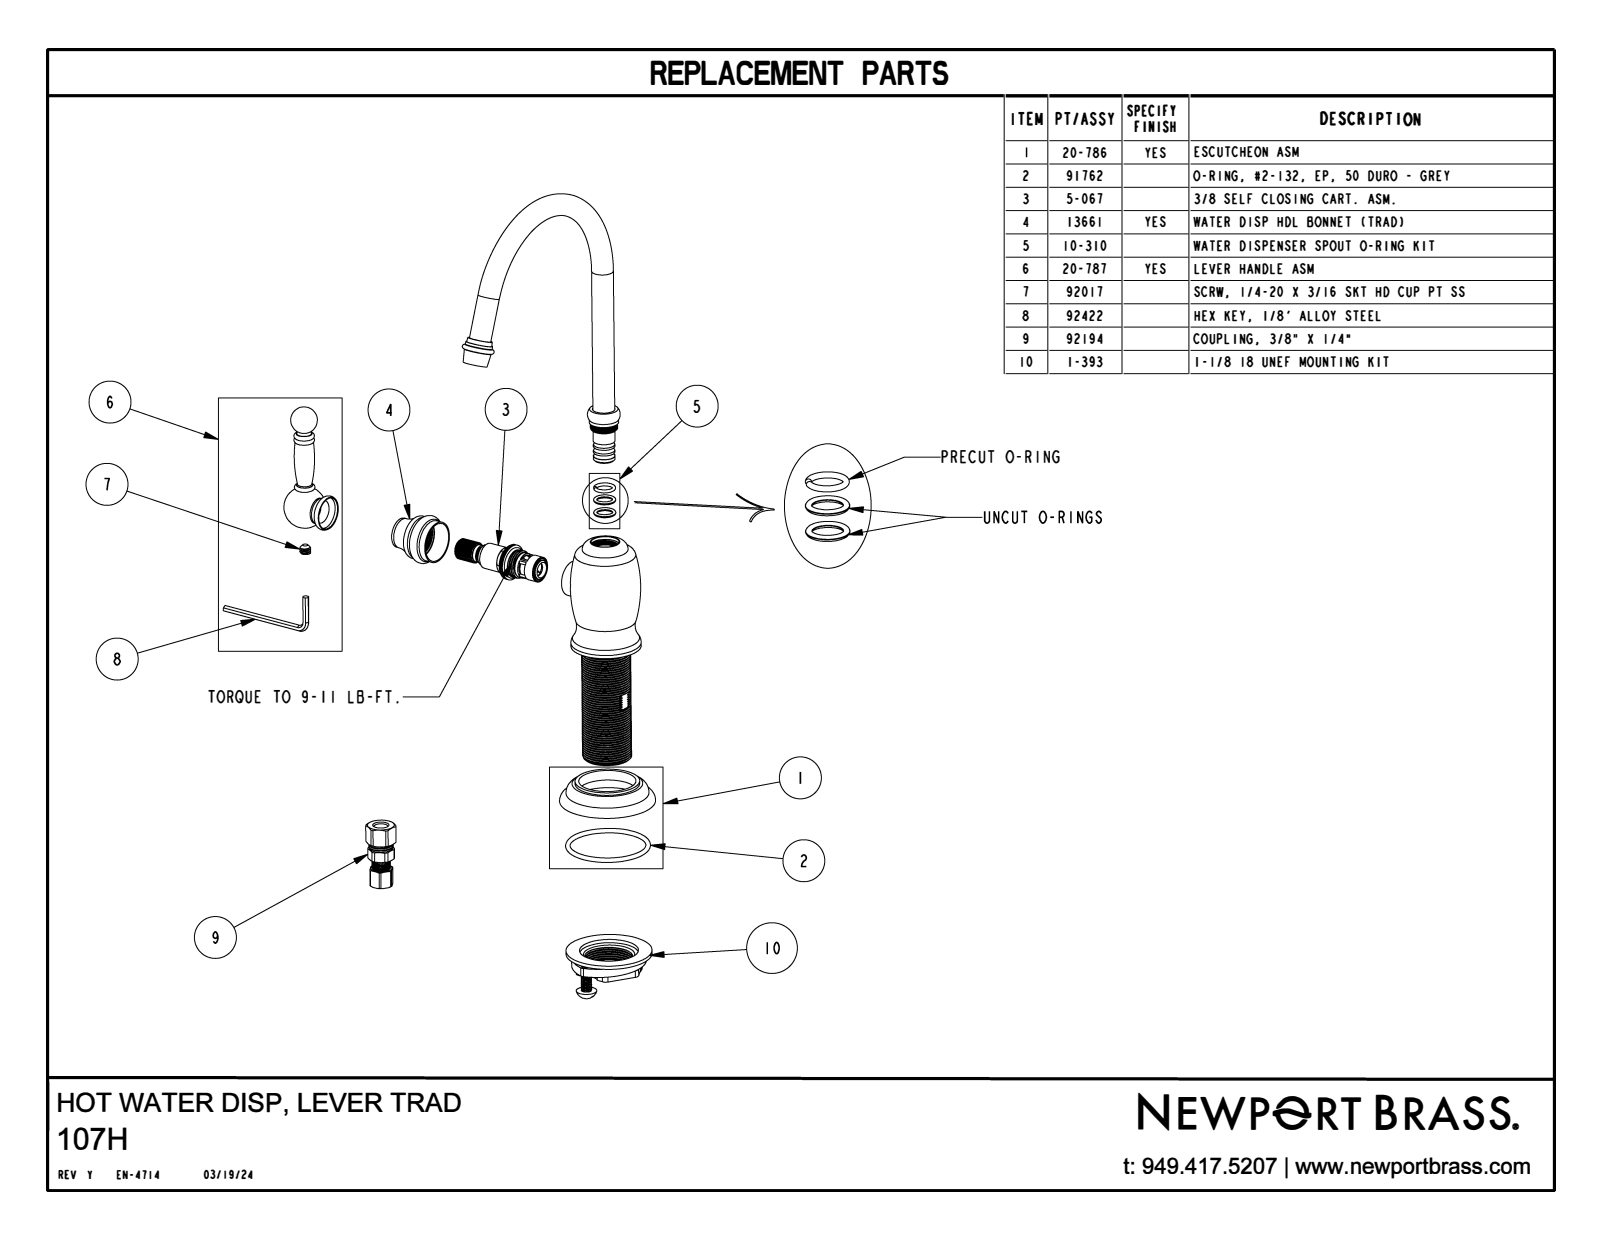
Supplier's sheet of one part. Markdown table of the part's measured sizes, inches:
| quantity | value |
| --- | --- |
| part name | 107H |
| STEP written by | CREO PARAMETRIC BY PTC INC, 2018400 (CONFIG_CONTROL_DESIGN) |
| units | inches |
| bodies | 1 solid, 88 faces (12 planar, 22 cylindrical, 54 other) |
| overall size | 9.512 × 6.182 × 3.828 |
| volume | 9.449 in³ |
| surface area | 49.26 in² |
| round holes (diameter × count) | 1 × 1 |
| round bosses / shafts (diameter × count) | 0.5 × 2, 1.61 × 1, 1.48 × 1, 0.95 × 1, 0.675 × 1, 0.625 × 1, 0.6 × 1, 0.36 × 1 |
| main face-to-face distances | 0.425, 0.43, 0.03, 3.312, 2.887, 2.882, 1, 1.03, 0.575, 0.475 |
